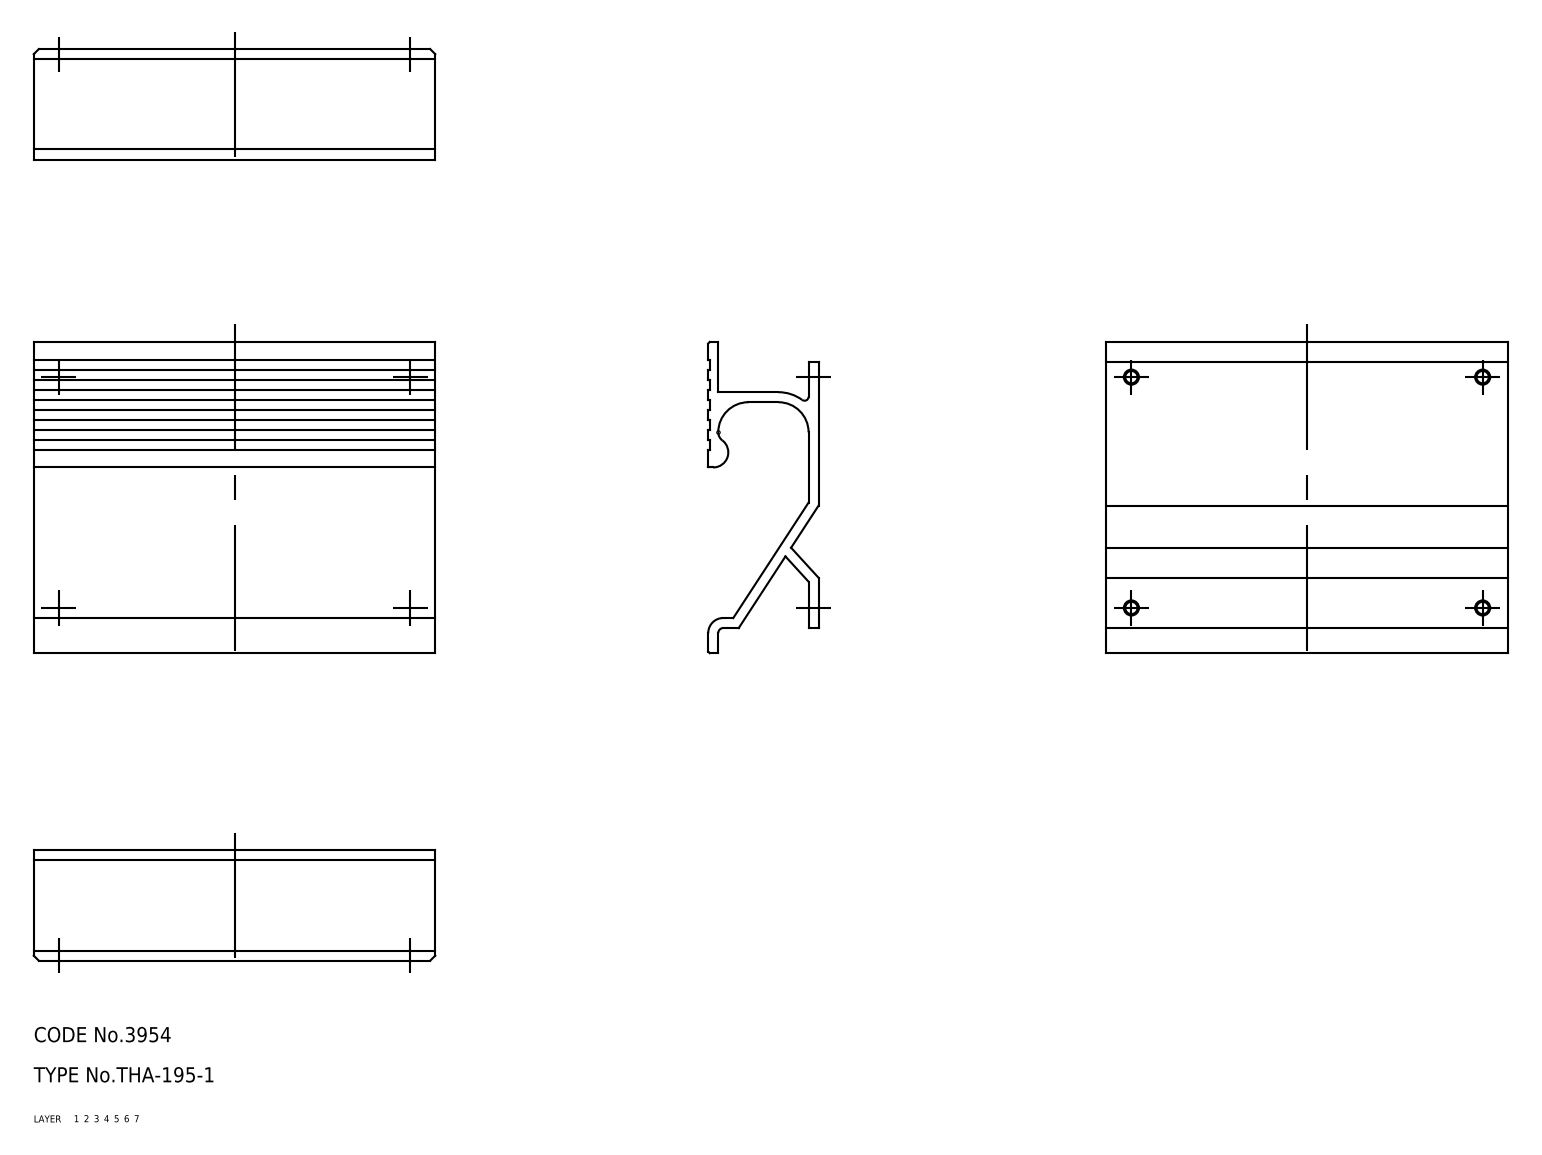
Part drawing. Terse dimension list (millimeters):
name: pull
written by: CADfix (AUTOMOTIVE_DESIGN)
unit: mm
bodies: 1 solid, 67 faces (0 planar, 0 cylindrical, 67 other)
size: 80 × 62 × 22
volume: 21 436 mm³; area: 21 087 mm²
